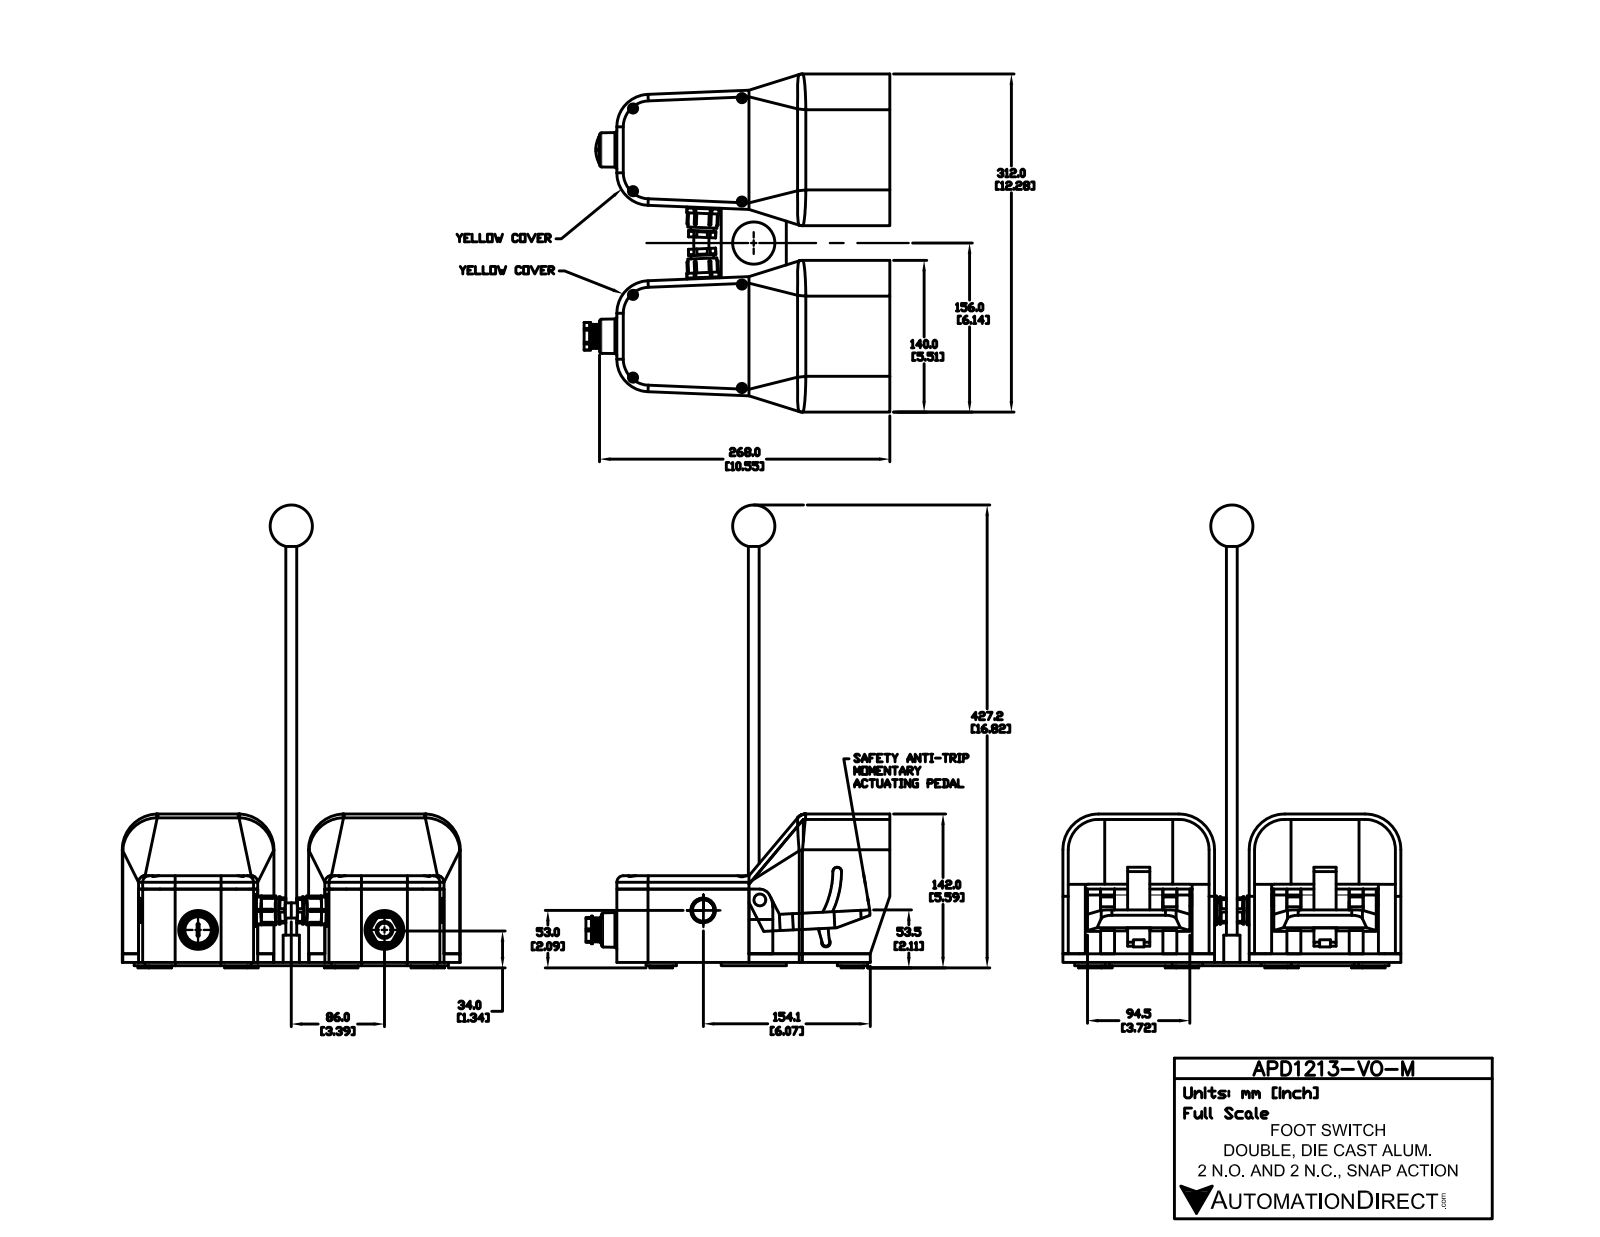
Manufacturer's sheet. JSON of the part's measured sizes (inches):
{"part_name": "APD1213-V0-M", "step_written_by": "SolidWorks 2015 (AUTOMOTIVE_DESIGN)", "units": "inches", "bodies": {"solids": 38, "faces": 865, "planar": 514, "cylindrical": 237, "other": 114}, "overall_size": [16.817, 12.283, 11.112], "volume_in3": 197.7, "surface_area_in2": 906.5, "round_holes": [[0.335, 8], [0.896, 4], [0.498, 1], [0.614, 1]], "round_bosses_or_shafts": [[1.102, 8], [0.827, 8], [0.782, 4], [1.171, 2], [1.051, 2], [0.992, 2], [0.846, 2], [1.004, 1]], "partial_cylinders_radius": [[0.039, 34], [0.042, 12], [0.394, 11], [0.236, 5], [1.102, 4], [1.181, 4], [1.299, 4], [0.787, 2]], "face_to_face_distances": [0.197, 5.315, 6.772, 0.315, 2.348, 5.512, 2.664, 2.349, 2.663, 0.118], "hole_center_spacings": [3.976, 5.206, 6.772, 3.004, 3.76, 5.211, 7.52, 8.172]}
